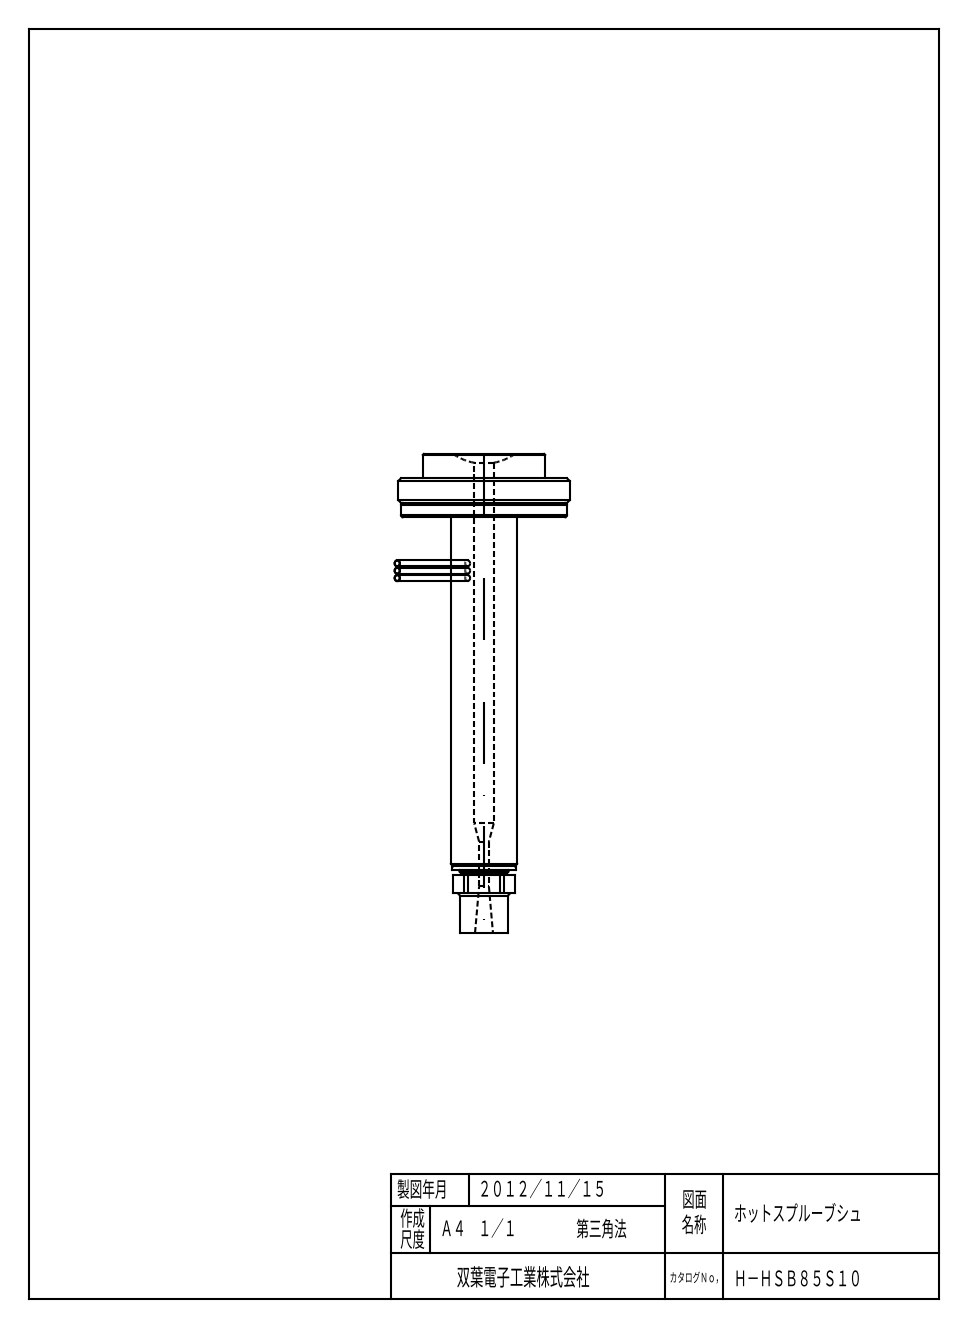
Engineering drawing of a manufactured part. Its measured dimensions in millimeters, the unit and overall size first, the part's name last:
Units: millimetres
Overall size (bounding box): 160.34 × 160.34 × 98
Round holes (diameter × count): ⌀5.5 ×4, ⌀8.9 ×4, ⌀4 ×1, ⌀16 ×1
Round bosses / shafts (diameter × count): ⌀4 ×3, ⌀1.2 ×3, ⌀35 ×1, ⌀34 ×1, ⌀13.5 ×1, ⌀13 ×1, ⌀12.7 ×1, ⌀10 ×1
Partial cylindrical surfaces — rounded edges, fillets, slot ends (radius × count): R12.5 ×1
Main face-to-face distances: 5, 8, 13, 7.5, 0.5, 5.5, 3, 73.1, 80.6, 81.1
Hole centre spacings: 12.5, 17.68, 25
Volume: 20 301 mm³ · Surface area: 10 208 mm²
Bodies: 1 solid, 78 faces (27 planar, 28 cylindrical, 23 other)
Part name (STEP PRODUCT): HSB85S10
STEP written by: SIEMENS PLM Software NX 2023 (AUTOMOTIVE_DESIGN)
